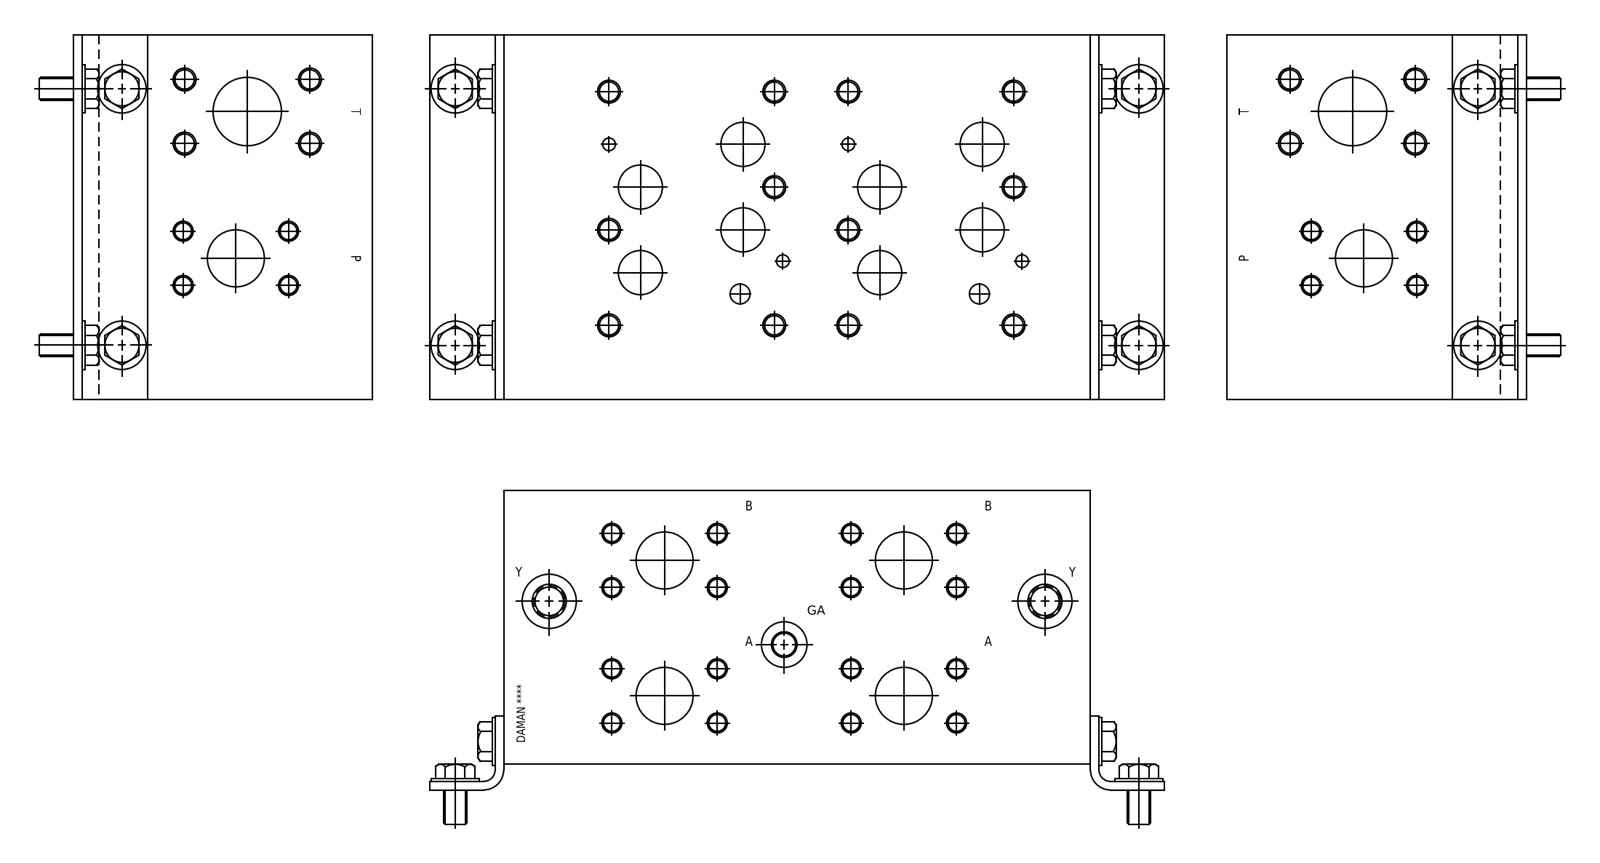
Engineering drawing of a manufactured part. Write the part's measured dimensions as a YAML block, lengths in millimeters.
part_name: "Part_DD08HP025F_3D"
step_written_by: "Autodesk Inventor 2019 (AUTOMOTIVE_DESIGN)"
units: millimeters
bodies: {solids: 1, faces: 775, planar: 411, cylindrical: 133, other: 231}
overall_size: [327.02, 203.2, 152.4]
volume: 9806000
surface_area: 372866
round_holes:
  - {diameter: 11.13, count: 25}
  - {diameter: 9.35, count: 23}
  - {diameter: 12.7, count: 20}
  - {diameter: 10.72, count: 18}
  - {diameter: 24.61, count: 8}
  - {diameter: 31.75, count: 5}
  - {diameter: 7.14, count: 4}
  - {diameter: 17.5, count: 2}
  - {diameter: 19.05, count: 2}
  - {diameter: 19.25, count: 2}
  - {diameter: 30.63, count: 2}
  - {diameter: 12.29, count: 1}
face_to_face_distances: [152.4, 203.2, 327.02, 0.79, 202.41, 30.23, 28.45, 27.66, 174.75, 122.17]
hole_center_spacings: [33.01, 133.35, 58.72, 66.02, 95.14, 30.18, 153.2, 74.63]
